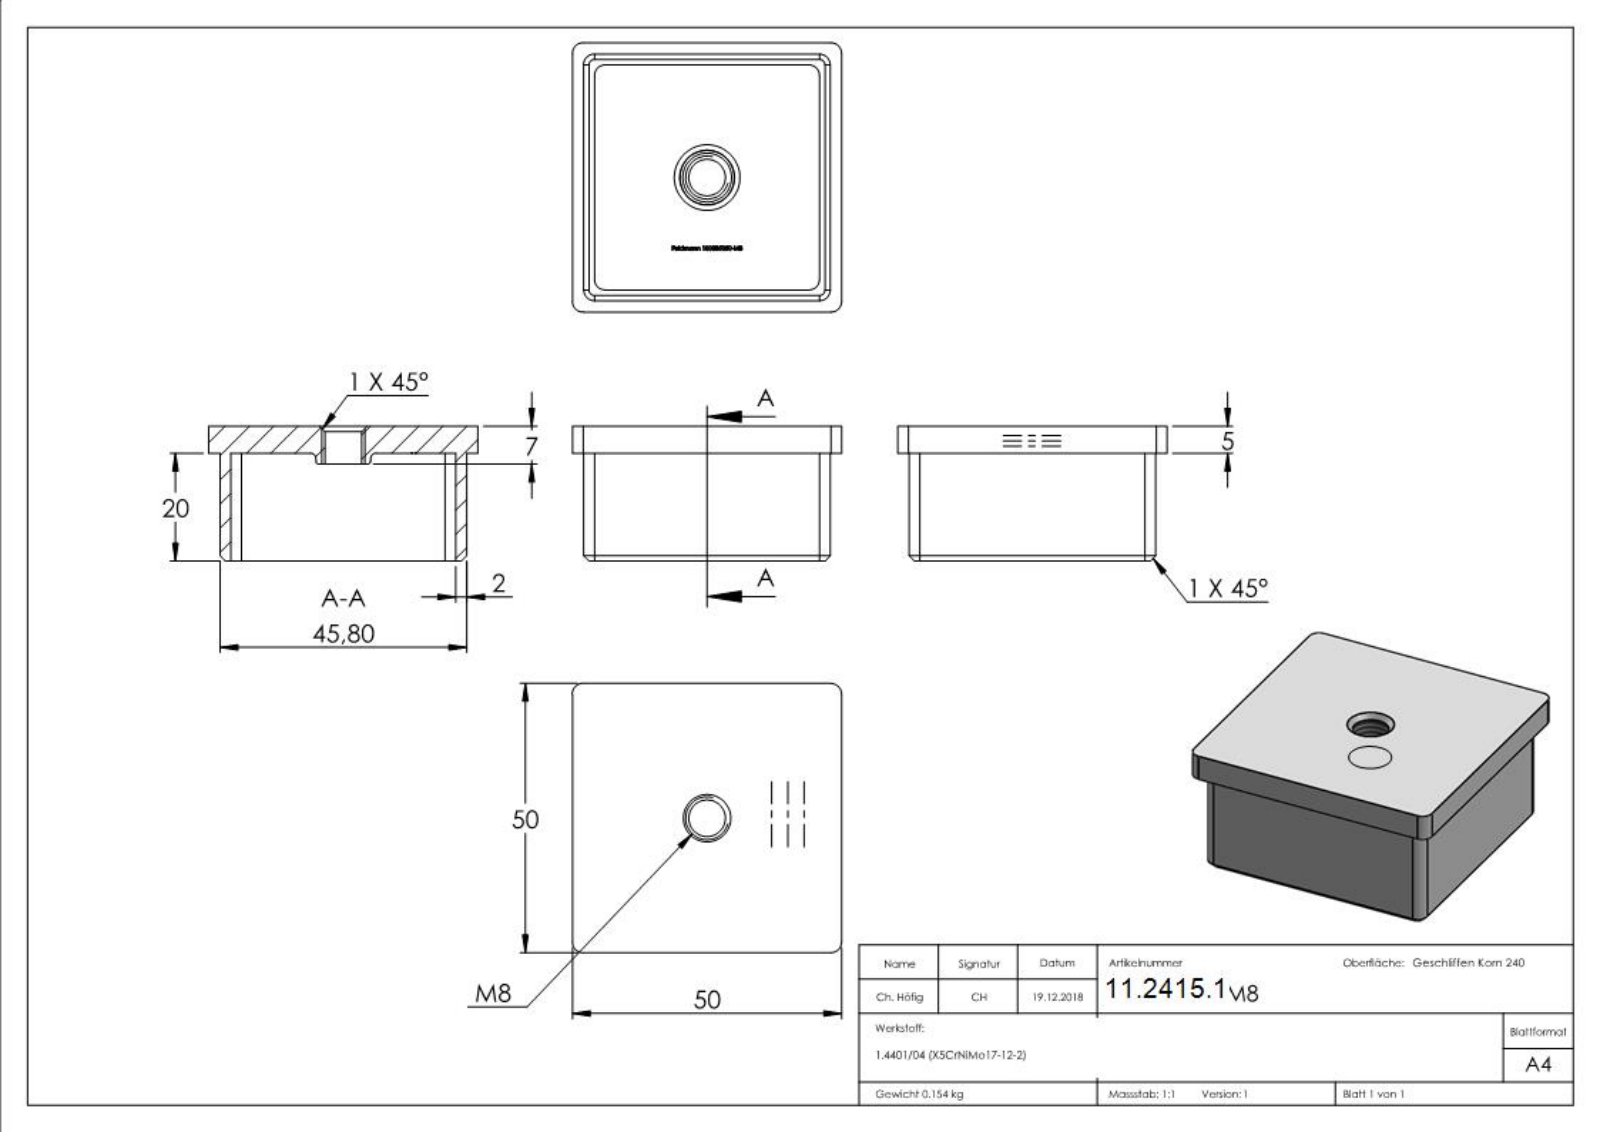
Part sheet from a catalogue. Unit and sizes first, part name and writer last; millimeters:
Units: millimetres
Overall size (bounding box): 50 × 50 × 25
Round holes (diameter × count): ⌀6.8 ×1
Partial cylindrical surfaces — rounded edges, fillets, slot ends (radius × count): R2 ×12
Main face-to-face distances: 2, 43.8, 5, 45.8, 41.8, 2.1, 4.1, 45.9, 47.9, 50
Volume: 19 303 mm³ · Surface area: 12 855 mm²
Bodies: 1 solid, 309 faces (143 planar, 14 cylindrical, 152 other)
Part name (STEP PRODUCT): 100035050-M8
STEP written by: SolidWorks 2015 (CONFIG_CONTROL_DESIGN)
